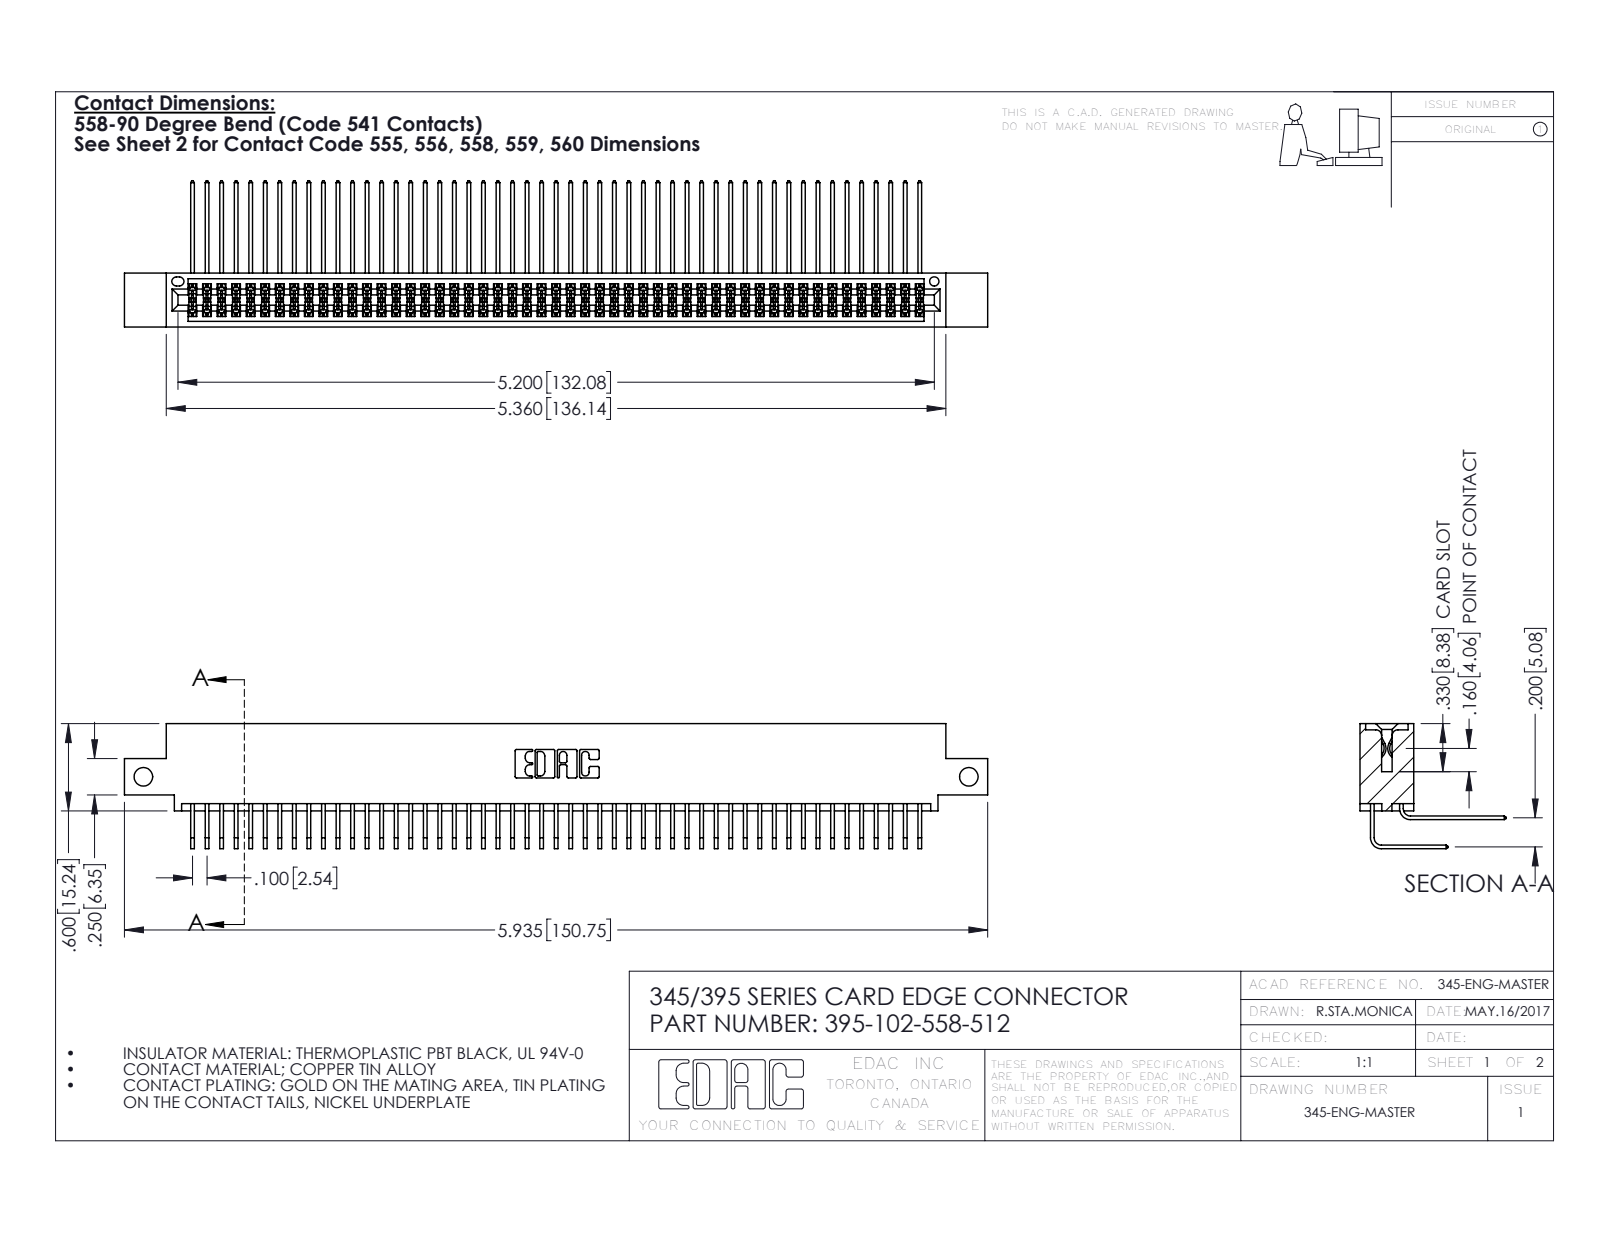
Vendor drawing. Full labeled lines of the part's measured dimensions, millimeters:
Part name (STEP PRODUCT): 345-292-001_558 559 Tail - 1; 395-102-558-512; 345-292-001_558 Tail - 2; 345 Part_0.110 Offset - Side Mount
STEP written by: SolidWorks 2016 (CONFIG_CONTROL_DESIGN)
Units: millimetres
Bodies: 103 solids, 5434 faces (3654 planar, 1780 cylindrical, 0 other)
Overall size (bounding box): 150.7 × 25.5 × 21.8
Volume: 15 200 mm³ · Surface area: 25 300 mm²
Round holes (diameter × count): ⌀3.3 ×2, ⌀1.6 ×1
Partial cylindrical surfaces — rounded edges, fillets, slot ends (radius × count): R0.2 ×154, R0.3 ×22, R0.2 ×6, R0.8 ×6, R0.7 ×3, R0.4 ×2, R0.5 ×2, R0.6 ×2
Main face-to-face distances: 1.8, 7.6, 5.1, 9.4, 2.5, 6.9, 0.6, 5.7, 0.6, 4.4
Hole centre spacings: 144.1
